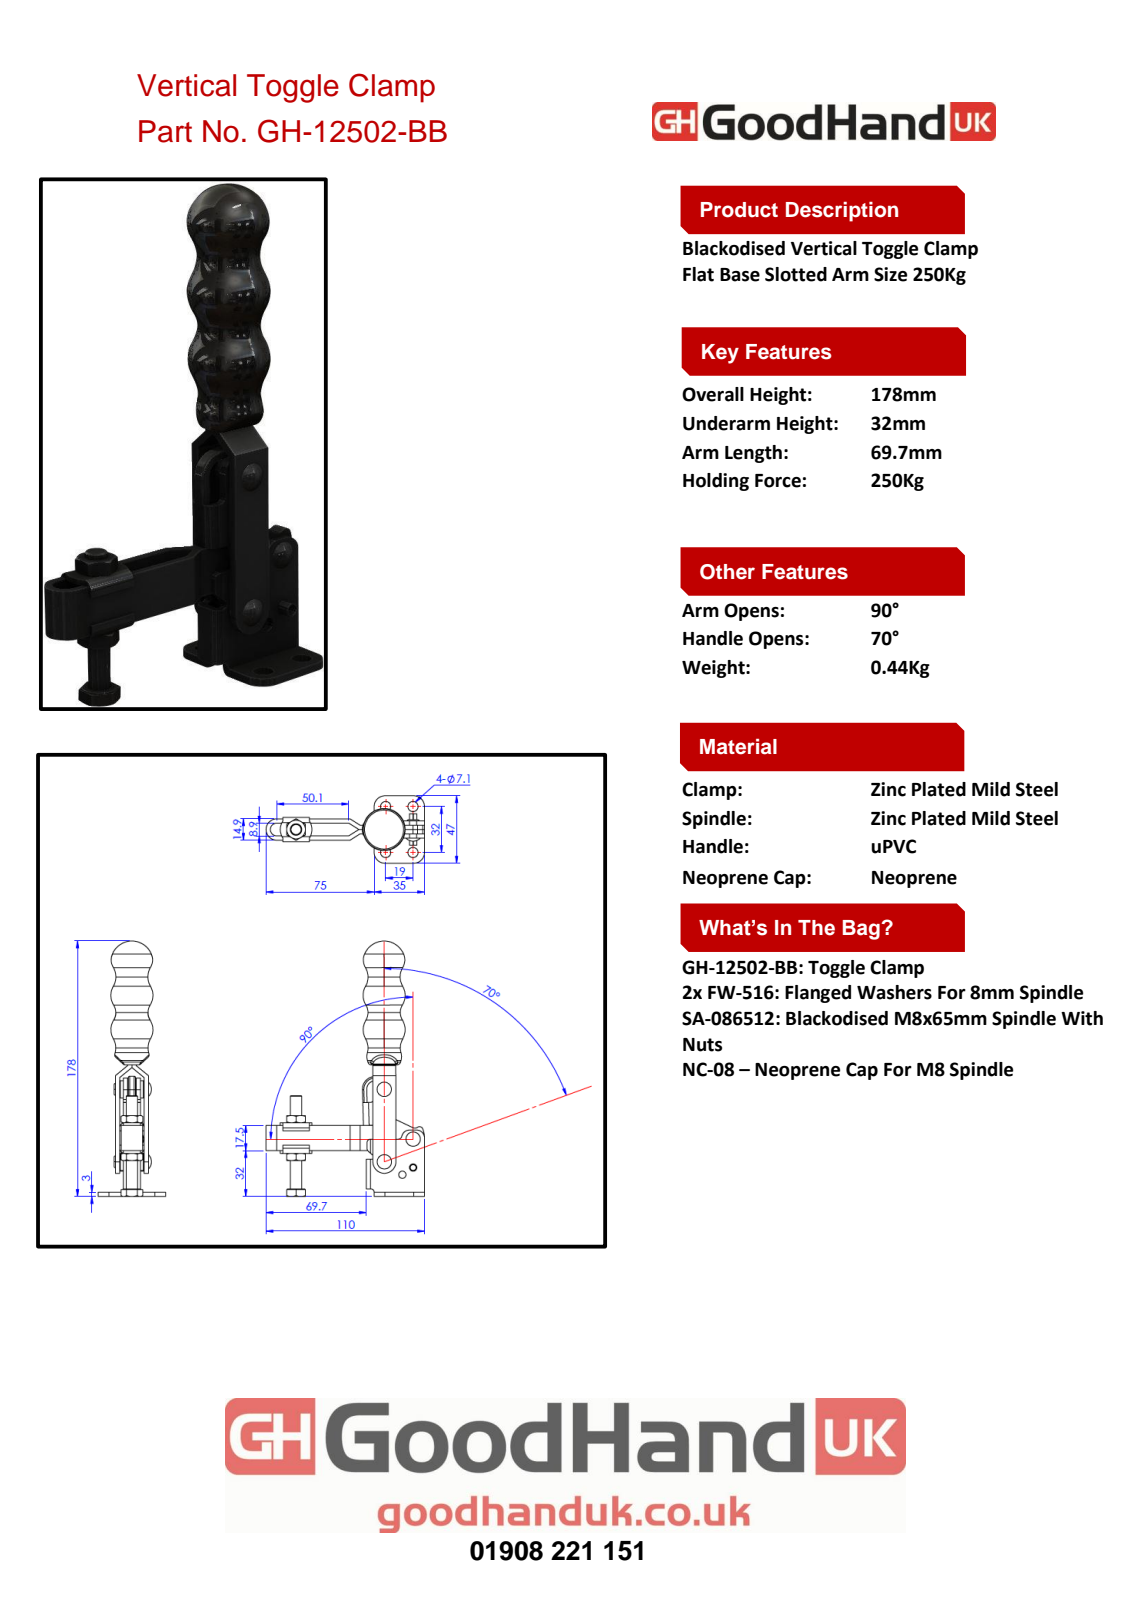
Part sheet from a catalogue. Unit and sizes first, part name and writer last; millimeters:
Units: millimetres
Overall size (bounding box): 177.49 × 110.3 × 47
Round holes (diameter × count): ⌀5 ×4, ⌀7.1 ×4, ⌀9.5 ×4, ⌀5.1 ×2, ⌀6.3 ×2, ⌀6.35 ×2, ⌀4.1 ×1, ⌀6.8 ×1, ⌀8 ×1, ⌀8.3 ×1
Round bosses / shafts (diameter × count): ⌀12 ×2, ⌀9.6 ×2, ⌀9.4 ×2, ⌀6.3 ×2, ⌀12.5 ×1
Partial cylindrical surfaces — rounded edges, fillets, slot ends (radius × count): R1 ×6, R3 ×5, R1.2 ×4, R2 ×4, R3.6 ×4, R7.5 ×4, R2.5 ×2, R4 ×2
Main face-to-face distances: 3, 6, 5.5, 8.5, 11.5, 14.5, 9, 15.95, 4.05, 1.45
Hole centre spacings: 19, 32, 37.22, 64.36, 82.9, 9.01, 15.4, 19.8
Volume: 76 099 mm³ · Surface area: 56 334 mm²
Bodies: 19 solids, 510 faces (167 planar, 201 cylindrical, 142 other)
Part name (STEP PRODUCT): 112502B13; fw516; 412502B37_1; 112502B01_1 (+8 more)
STEP written by: SolidWorks 2016 (AUTOMOTIVE_DESIGN)
